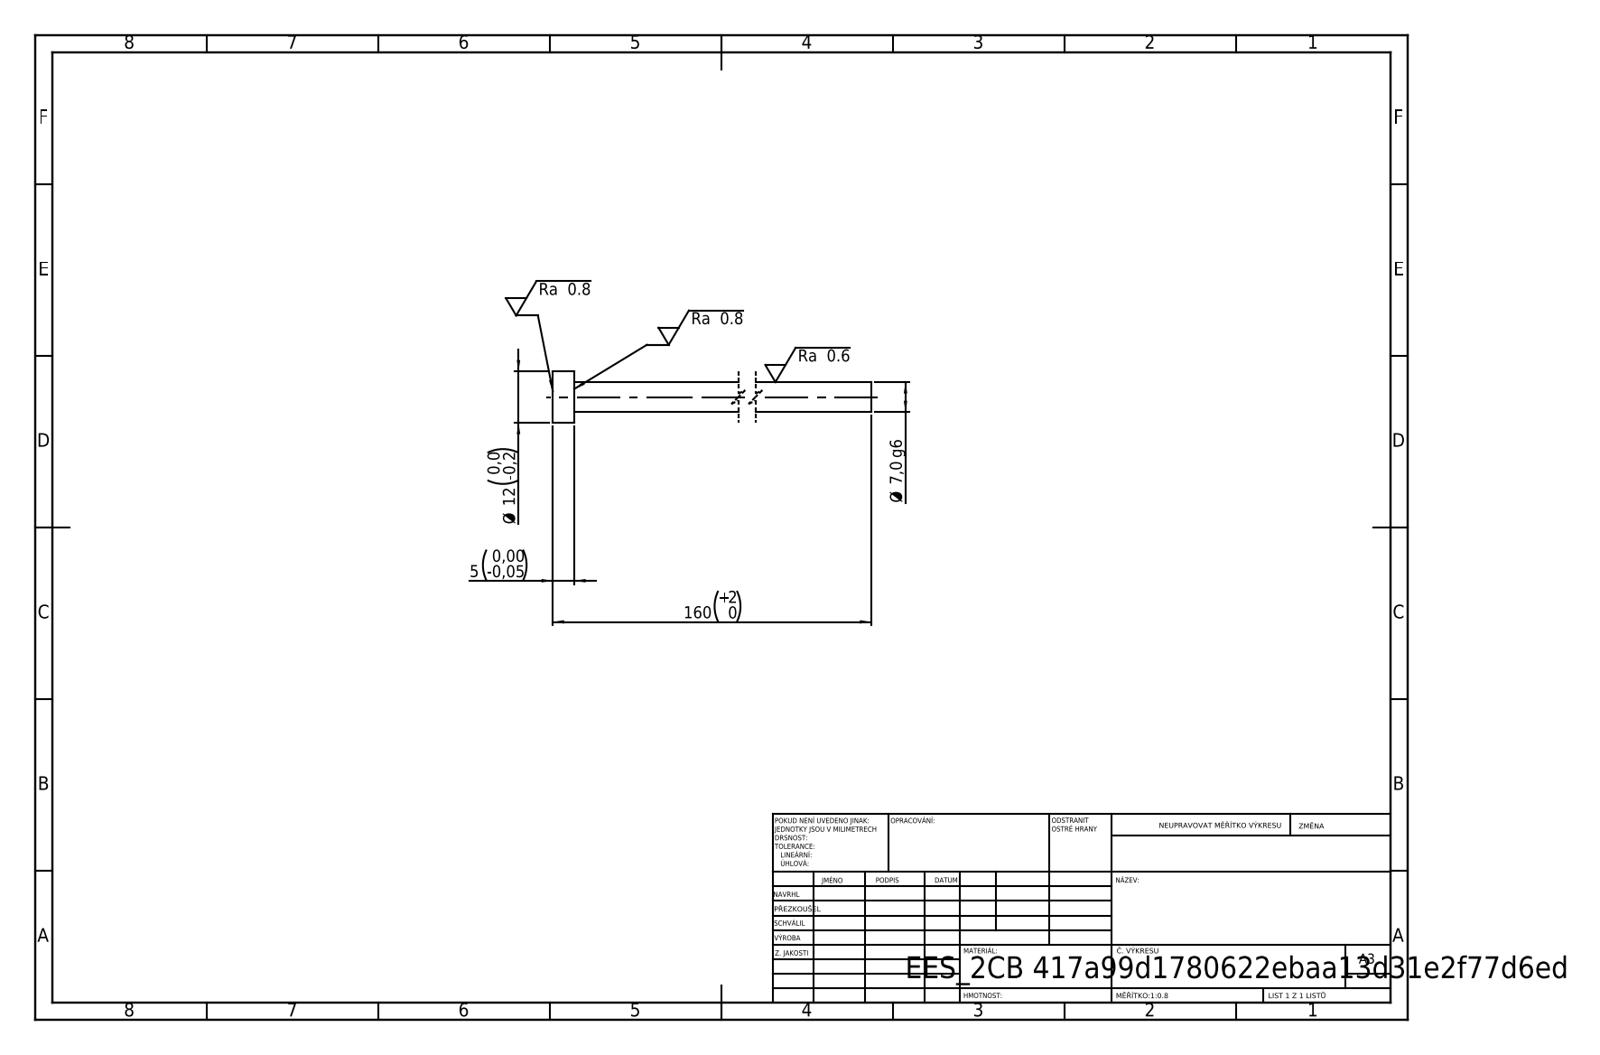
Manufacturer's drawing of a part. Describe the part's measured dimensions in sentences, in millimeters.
Its 3-D file was written by "SolidWorks 2019 (CONFIG_CONTROL_DESIGN)". It is 1 solid with 7 faces: 3 planar, 4 cylindrical and 0 other. Overall it measures 160 by 12 by 12 millimeters. Its volume is 6 531 cubic millimeters and its surface area 3 823 square millimeters. Round bosses or shafts: 1 of diameter 12, 1 of diameter 7. The main face-to-face distances are 5, 160, 155.
